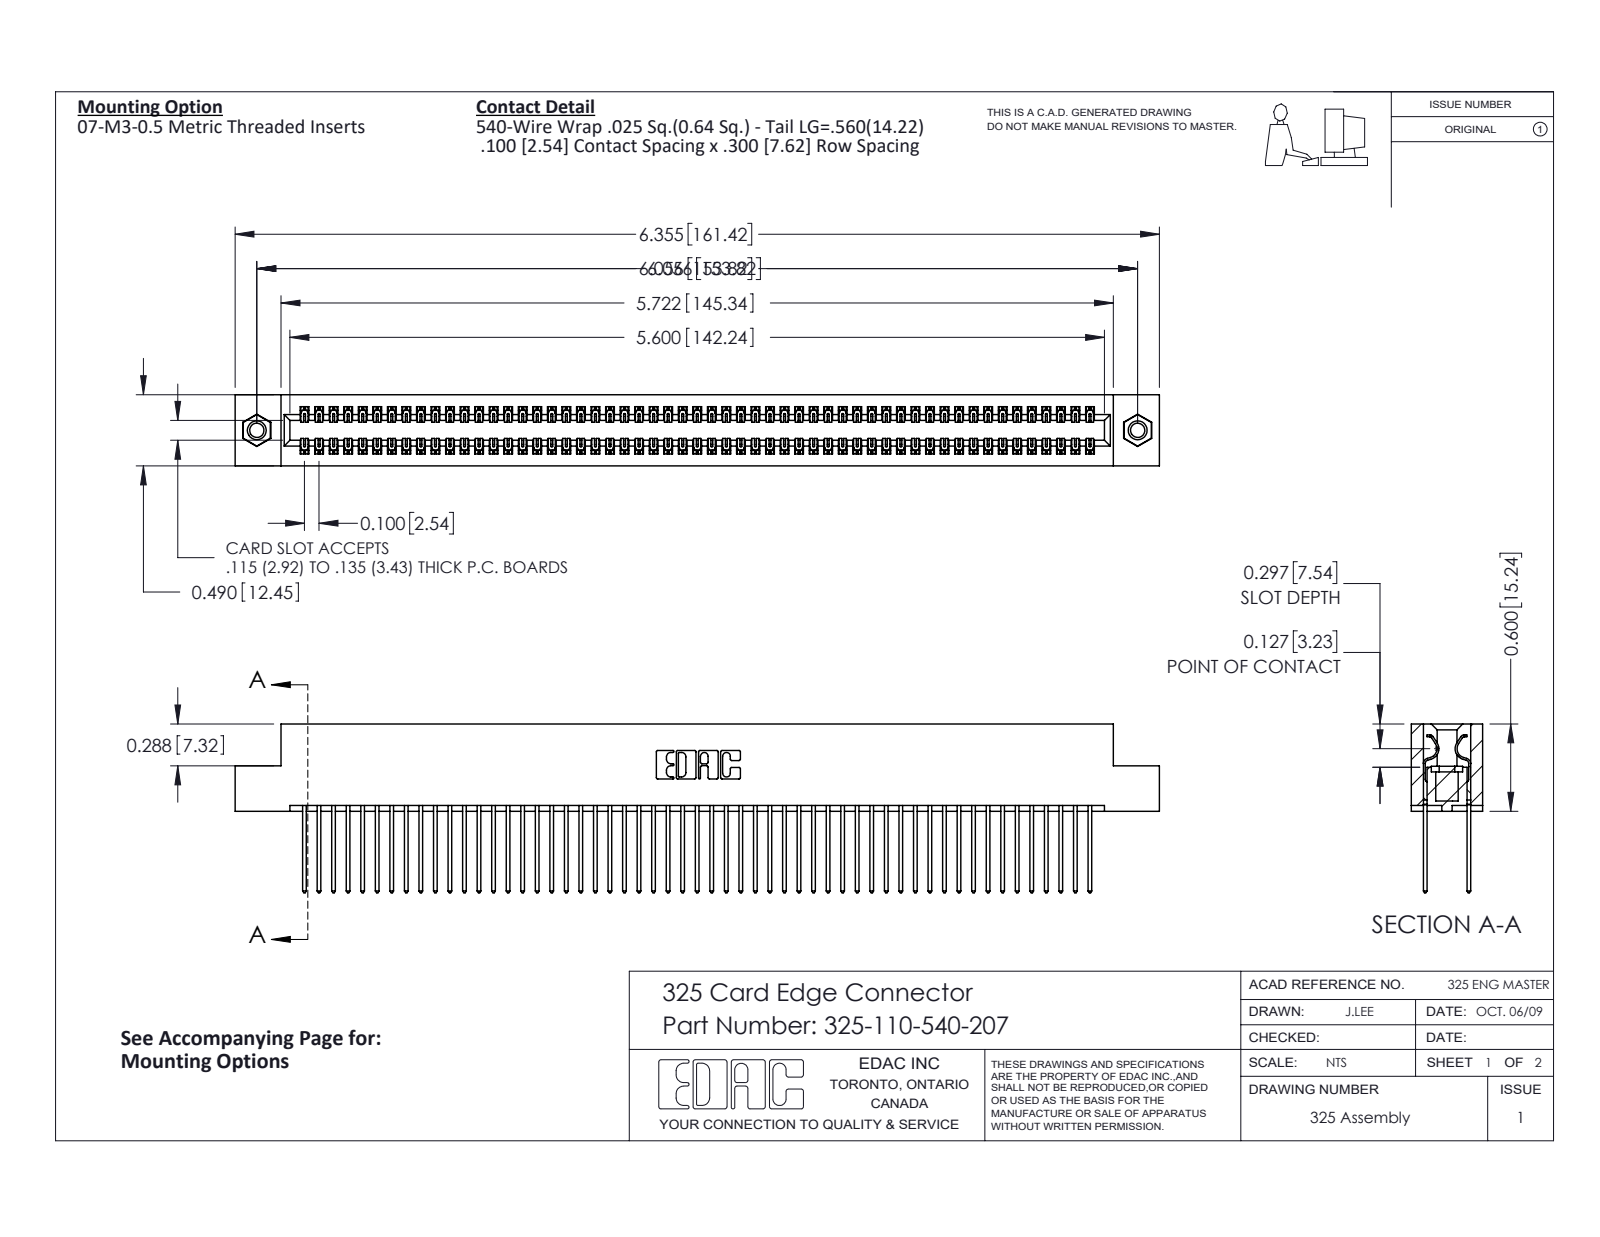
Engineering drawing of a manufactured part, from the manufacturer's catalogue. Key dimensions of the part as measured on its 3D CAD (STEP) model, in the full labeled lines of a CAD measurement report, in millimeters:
Part name (STEP PRODUCT): 345-250-001_345-250-005-103; 325-110-540-207; 325 Part_TI; 325-292-001_325-293-140
STEP written by: SolidWorks 2016 (CONFIG_CONTROL_DESIGN)
Units: millimetres
Bodies: 113 solids, 5894 faces (4062 planar, 1816 cylindrical, 16 other)
Overall size (bounding box): 161.4 × 29.5 × 12.4
Volume: 21 350 mm³ · Surface area: 28 170 mm²
Round holes (diameter × count): ⌀2.5 ×2, ⌀3.2 ×2, ⌀4.1 ×2
Round bosses / shafts (diameter × count): ⌀3.9 ×2
Partial cylindrical surfaces — rounded edges, fillets, slot ends (radius × count): R0.2 ×165, R0.3 ×110, R0.3 ×22, R0.2 ×6, R0.8 ×6, R0.7 ×3, R0.4 ×2, R0.6 ×2
Main face-to-face distances: 2.1, 10.3, 7.6, 2.7, 9.7, 0.6, 8.3, 12.4, 7, 14.2
Hole centre spacings: 153.8
